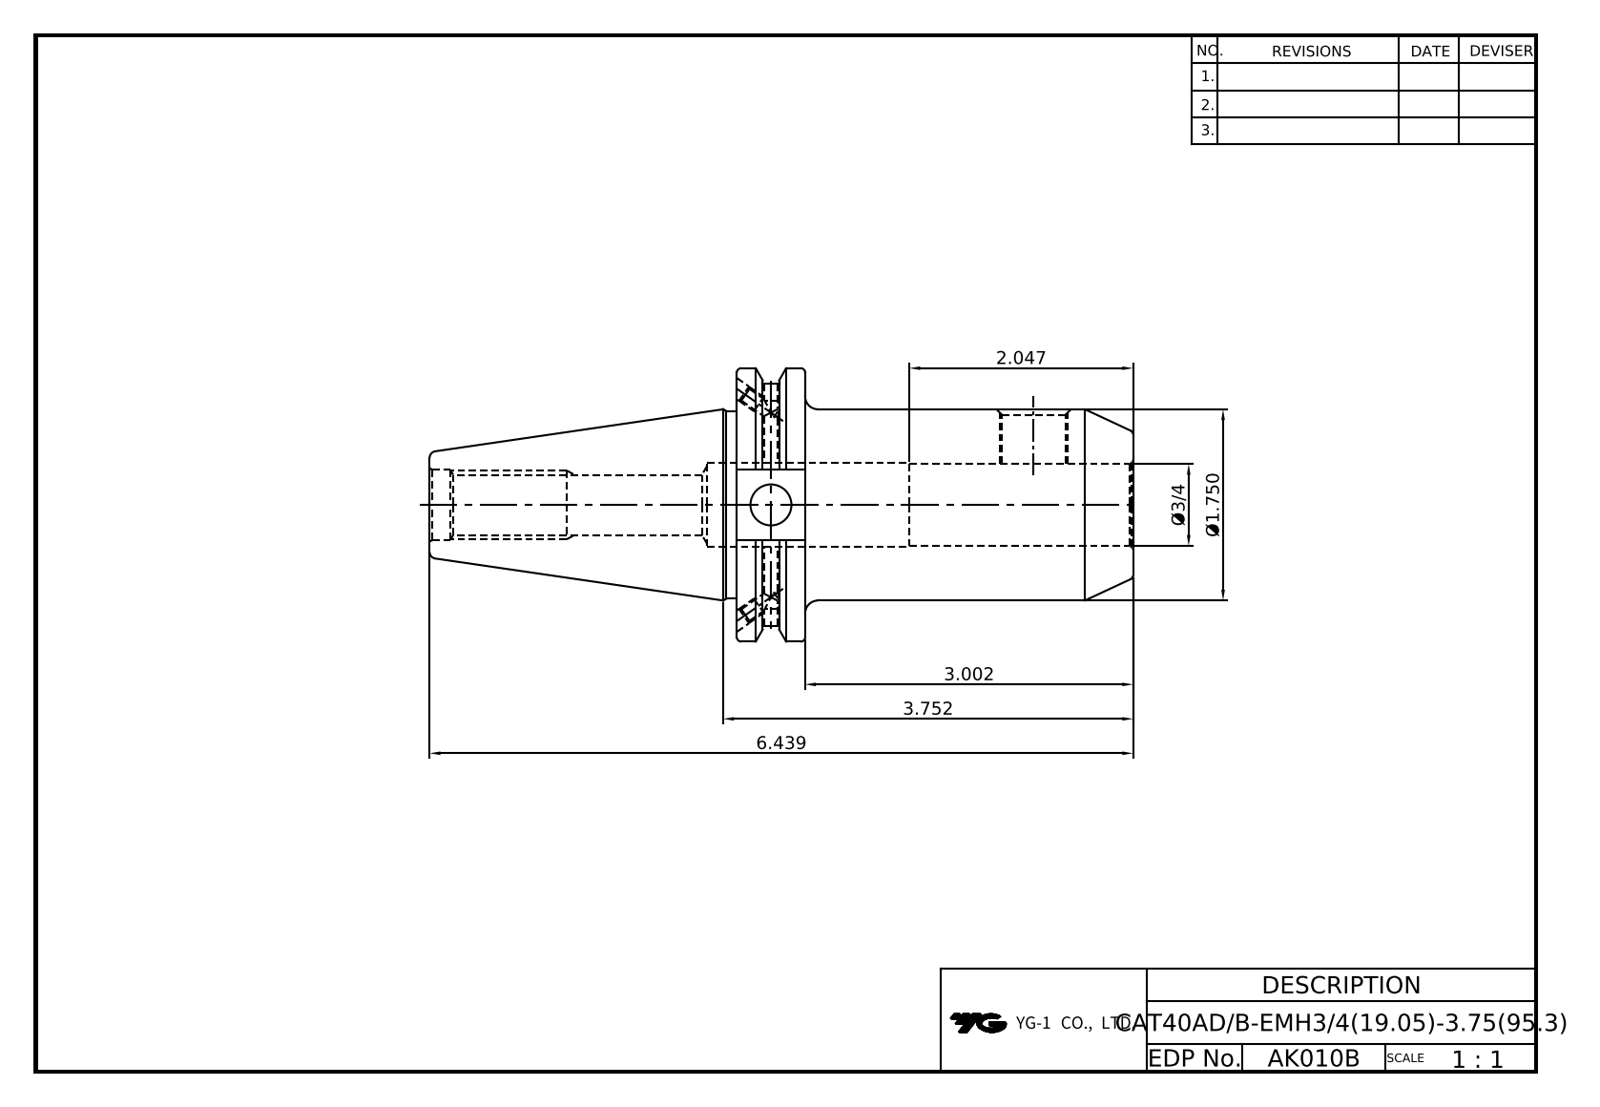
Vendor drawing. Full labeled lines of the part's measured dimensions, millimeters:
Part name (STEP PRODUCT): LO-CAT40ADB-EMH19.05-95.3
STEP written by: Autodesk Inventor 2020 (AUTOMOTIVE_DESIGN)
Units: millimetres
Bodies: 1 solid, 89 faces (39 planar, 28 cylindrical, 22 other)
Overall size (bounding box): 163.55 × 63.5 × 61.09
Volume: 190 392 mm³ · Surface area: 35 591 mm²
Round holes (diameter × count): ⌀3.24 ×4, ⌀4 ×2, ⌀4.2 ×2, ⌀9.53 ×1, ⌀13.39 ×1, ⌀14.35 ×1, ⌀16.3 ×1, ⌀19.05 ×1, ⌀19.65 ×1
Round bosses / shafts (diameter × count): ⌀63.5 ×1, ⌀44.45 ×1, ⌀43.6 ×1
Partial cylindrical surfaces — rounded edges, fillets, slot ends (radius × count): R28.15 ×1
Main face-to-face distances: 15.88, 92.13, 76.25, 47.6, 16.38, 71.42, 87.3, 163.55, 77.47, 6.05
